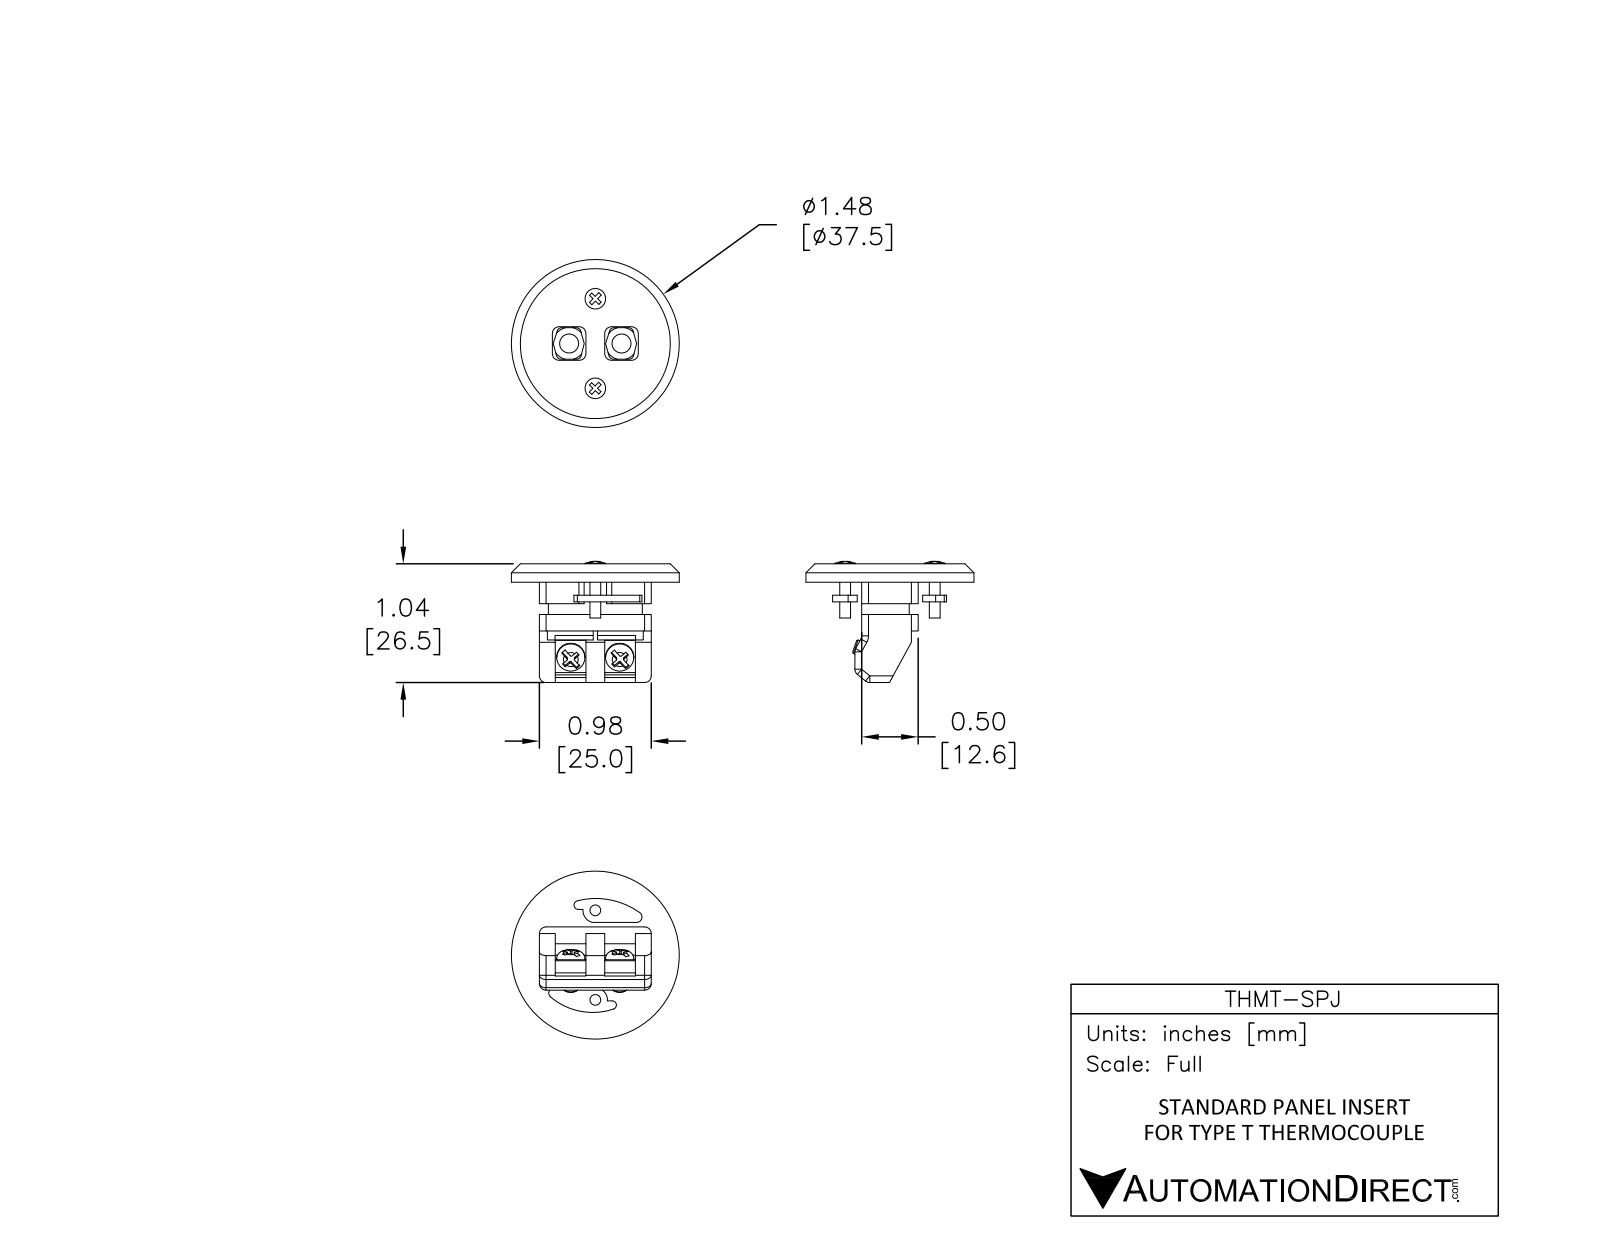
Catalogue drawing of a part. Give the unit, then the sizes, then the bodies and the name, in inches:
Units: inches
Overall size (bounding box): 1.476 × 1.476 × 1.065
Round holes (diameter × count): ⌀0.167 ×2
Round bosses / shafts (diameter × count): ⌀0.248 ×2, ⌀0.181 ×2, ⌀0.126 ×2, ⌀0.094 ×2, ⌀1.476 ×1
Partial cylindrical surfaces — rounded edges, fillets, slot ends (radius × count): R0.059 ×24, R0.01 ×8, R0.039 ×8, R0.036 ×1, R0.039 ×1, R0.046 ×1, R0.048 ×1, R0.106 ×1
Main face-to-face distances: 0.161, 0.079, 0.496, 0.984, 0.059, 0.276, 0.429, 0.591, 0.335, 0.039
Hole centre spacings: 0.461
Volume: 0.584 in³ · Surface area: 8.784 in²
Bodies: 1 solid, 310 faces (201 planar, 85 cylindrical, 24 other)
Part name (STEP PRODUCT): THMT-SPJ
STEP written by: SolidWorks 2017 (AUTOMOTIVE_DESIGN)
